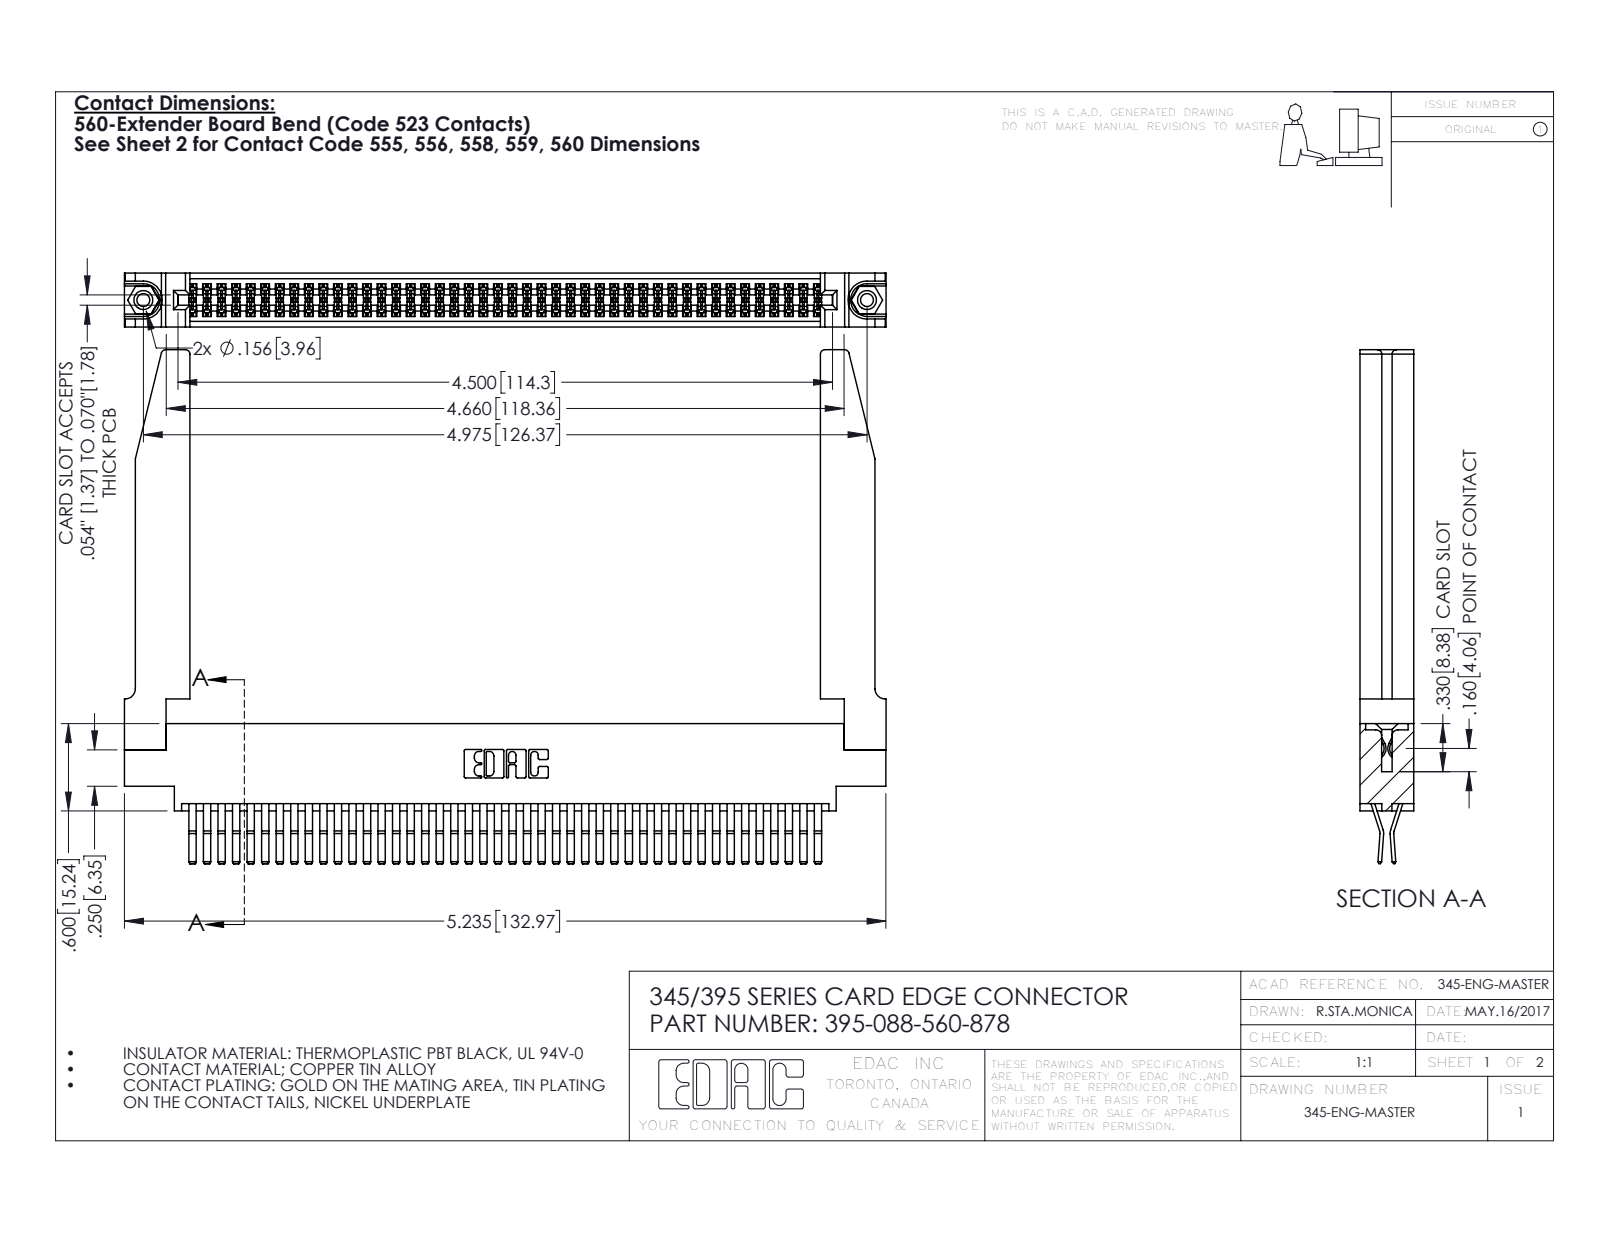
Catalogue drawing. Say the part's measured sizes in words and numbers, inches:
The part is named "345-292-001_560 Tail; 345-250-001_345-250-001-102; 345 Part_0.170 Offset - 0.156 Dia-TH; 395-088-560-878 (+1 more)". Its 3-D file was written by "SolidWorks 2016 (CONFIG_CONTROL_DESIGN)". It is 93 solids with 4940 faces: 3130 planar, 1758 cylindrical and 52 other. Overall it measures 5.236 by 3.532 by 0.37 inches. Its volume is 1.292 cubic inches and its surface area 43.89 square inches. Round holes: 2 of diameter 0.089, 2 of diameter 0.125, 2 of diameter 0.156, 1 of diameter 0.064. Round bosses or shafts: 2 of diameter 0.155. Partial cylindrical surfaces (rounded edges, fillets, slot ends): 132 of radius 0.006, 22 of radius 0.01, 8 of radius 0.03, 6 of radius 0.007, 6 of radius 0.031, 3 of radius 0.026, 2 of radius 0.01, 2 of radius 0.014. The main face-to-face distances are 0.37, 0.072, 0.298, 0.025, 0.2, 0.098, 0.272, 0.225, 0.175, 0.148. The hole center spacings are 0.27, 4.739, 4.975.
